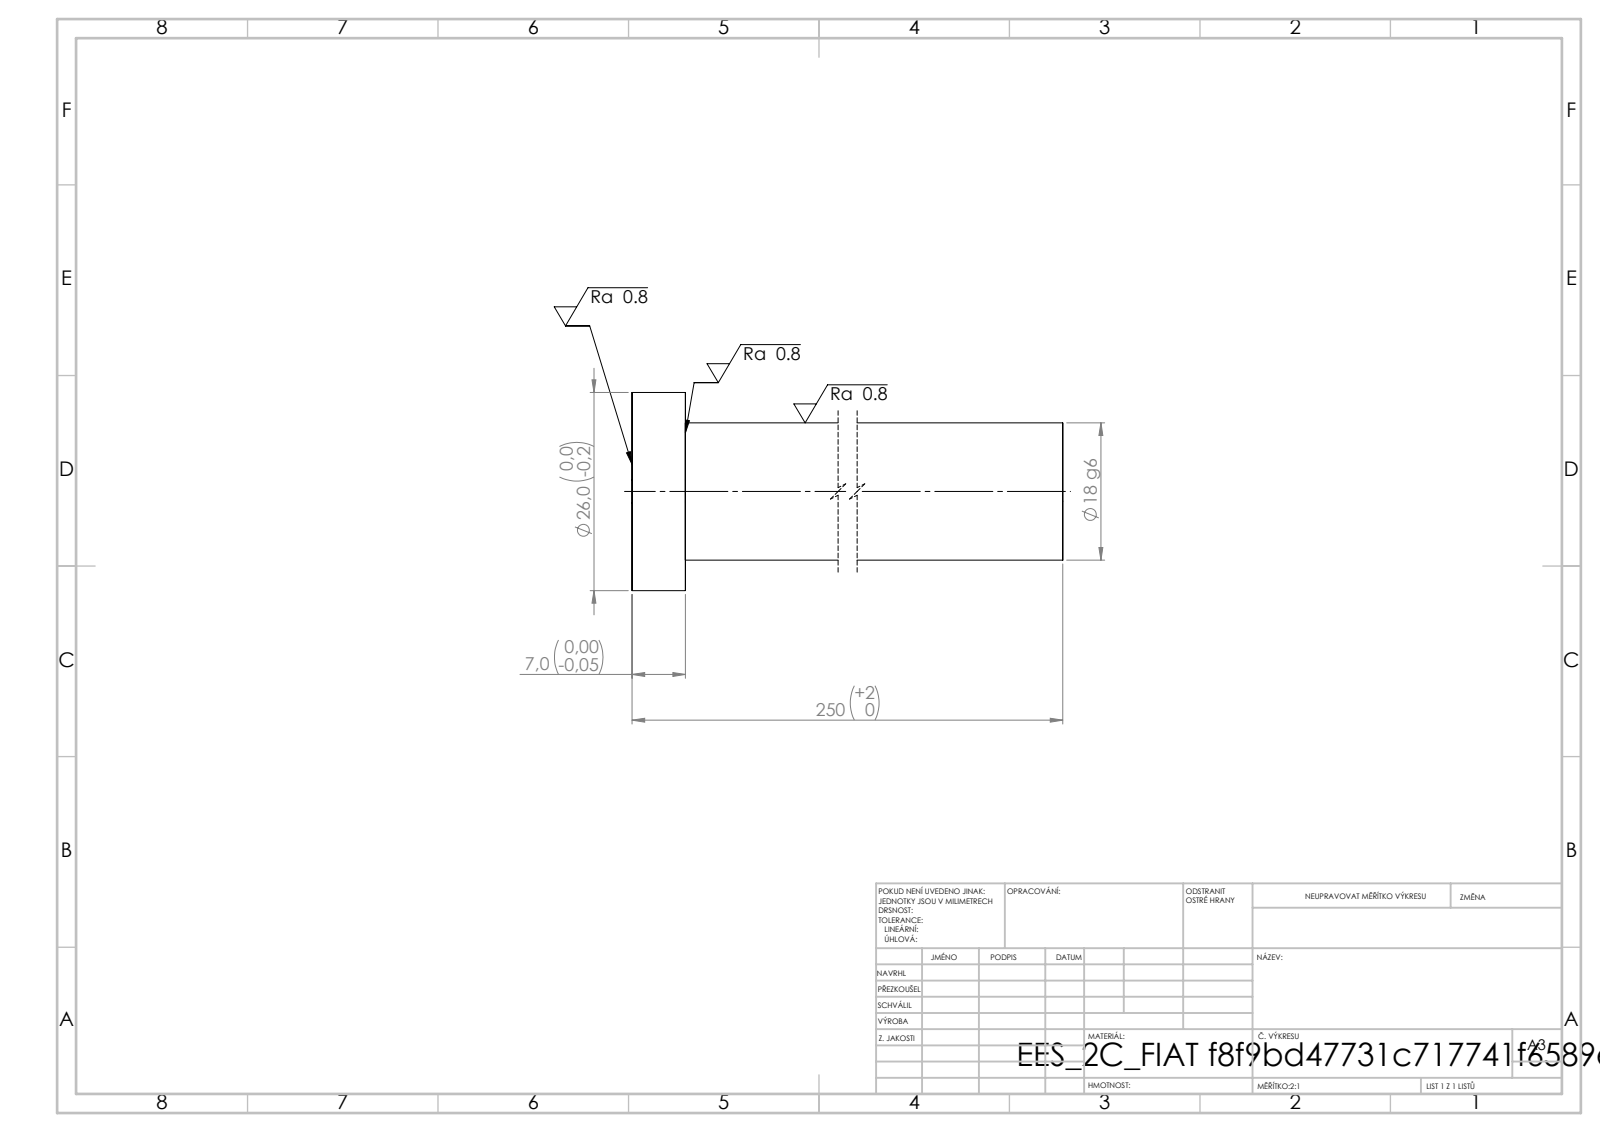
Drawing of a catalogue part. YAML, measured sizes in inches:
step_written_by: "SolidWorks 2019 (CONFIG_CONTROL_DESIGN)"
units: inches
bodies: {solids: 1, faces: 7, planar: 3, cylindrical: 4, other: 0}
overall_size: [9.843, 1.024, 1.024]
volume: 4
surface_area: 23.83
round_bosses_or_shafts:
  - {diameter: 1.024, count: 1}
  - {diameter: 0.709, count: 1}
face_to_face_distances: [0.276, 9.843, 9.567]
